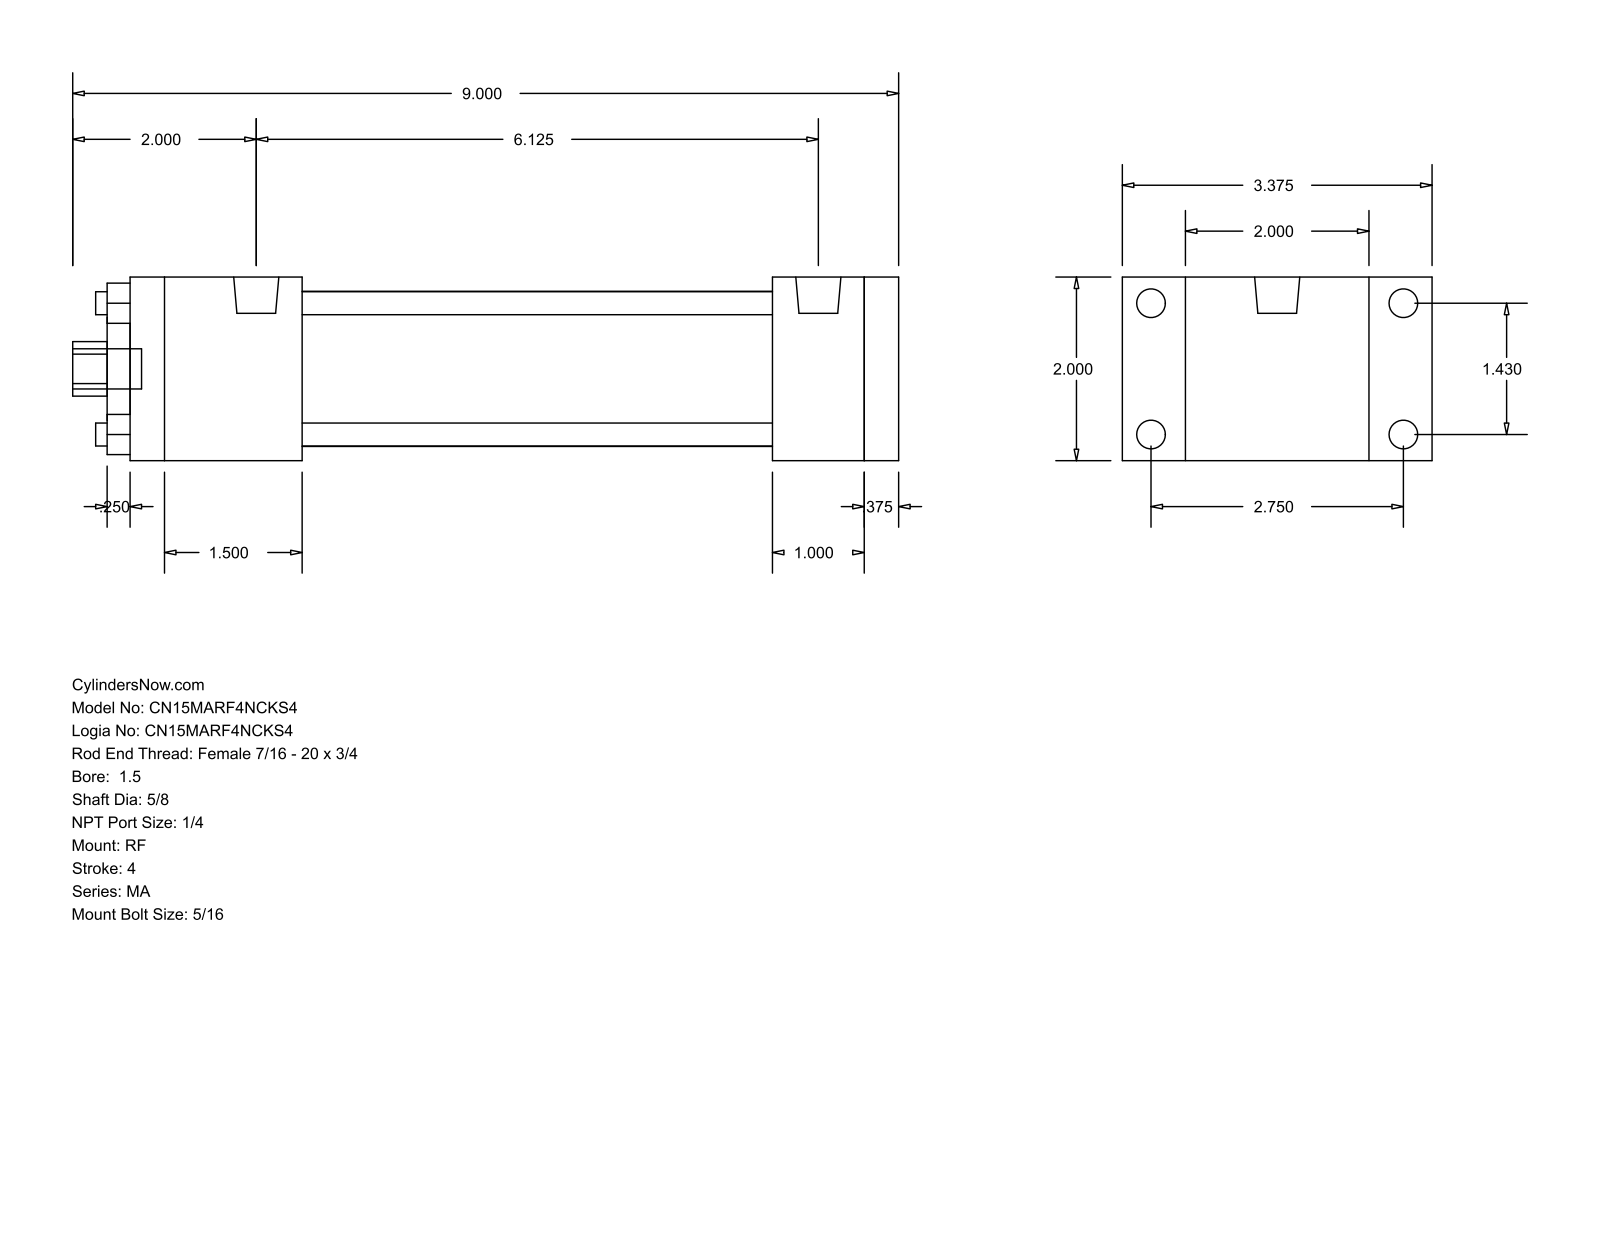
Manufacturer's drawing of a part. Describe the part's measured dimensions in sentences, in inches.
The part is named "MA_RF__0150_0.625". Its 3-D file was written by "GSSL Pune (CONFIG_CONTROL_DESIGN)". It is 0 solids with 92 faces: 64 planar, 28 cylindrical and 0 other. Overall it measures 9 by 3.375 by 2 inches. Round holes: 4 of diameter 0.25, 1 of diameter 0.625, 1 of diameter 1.125, 1 of diameter 1.69. Round bosses or shafts: 8 of diameter 0.313, 2 of diameter 0.492, 1 of diameter 0.437. Partial cylindrical surfaces (rounded edges, fillets, slot ends): 1 of radius 0.297. The main face-to-face distances are 2, 0.375, 8.375, 8, 7, 1, 1.375, 1.875, 5.125, 6.125. The hole center spacings are 1.011, 1.43, 2.022.
